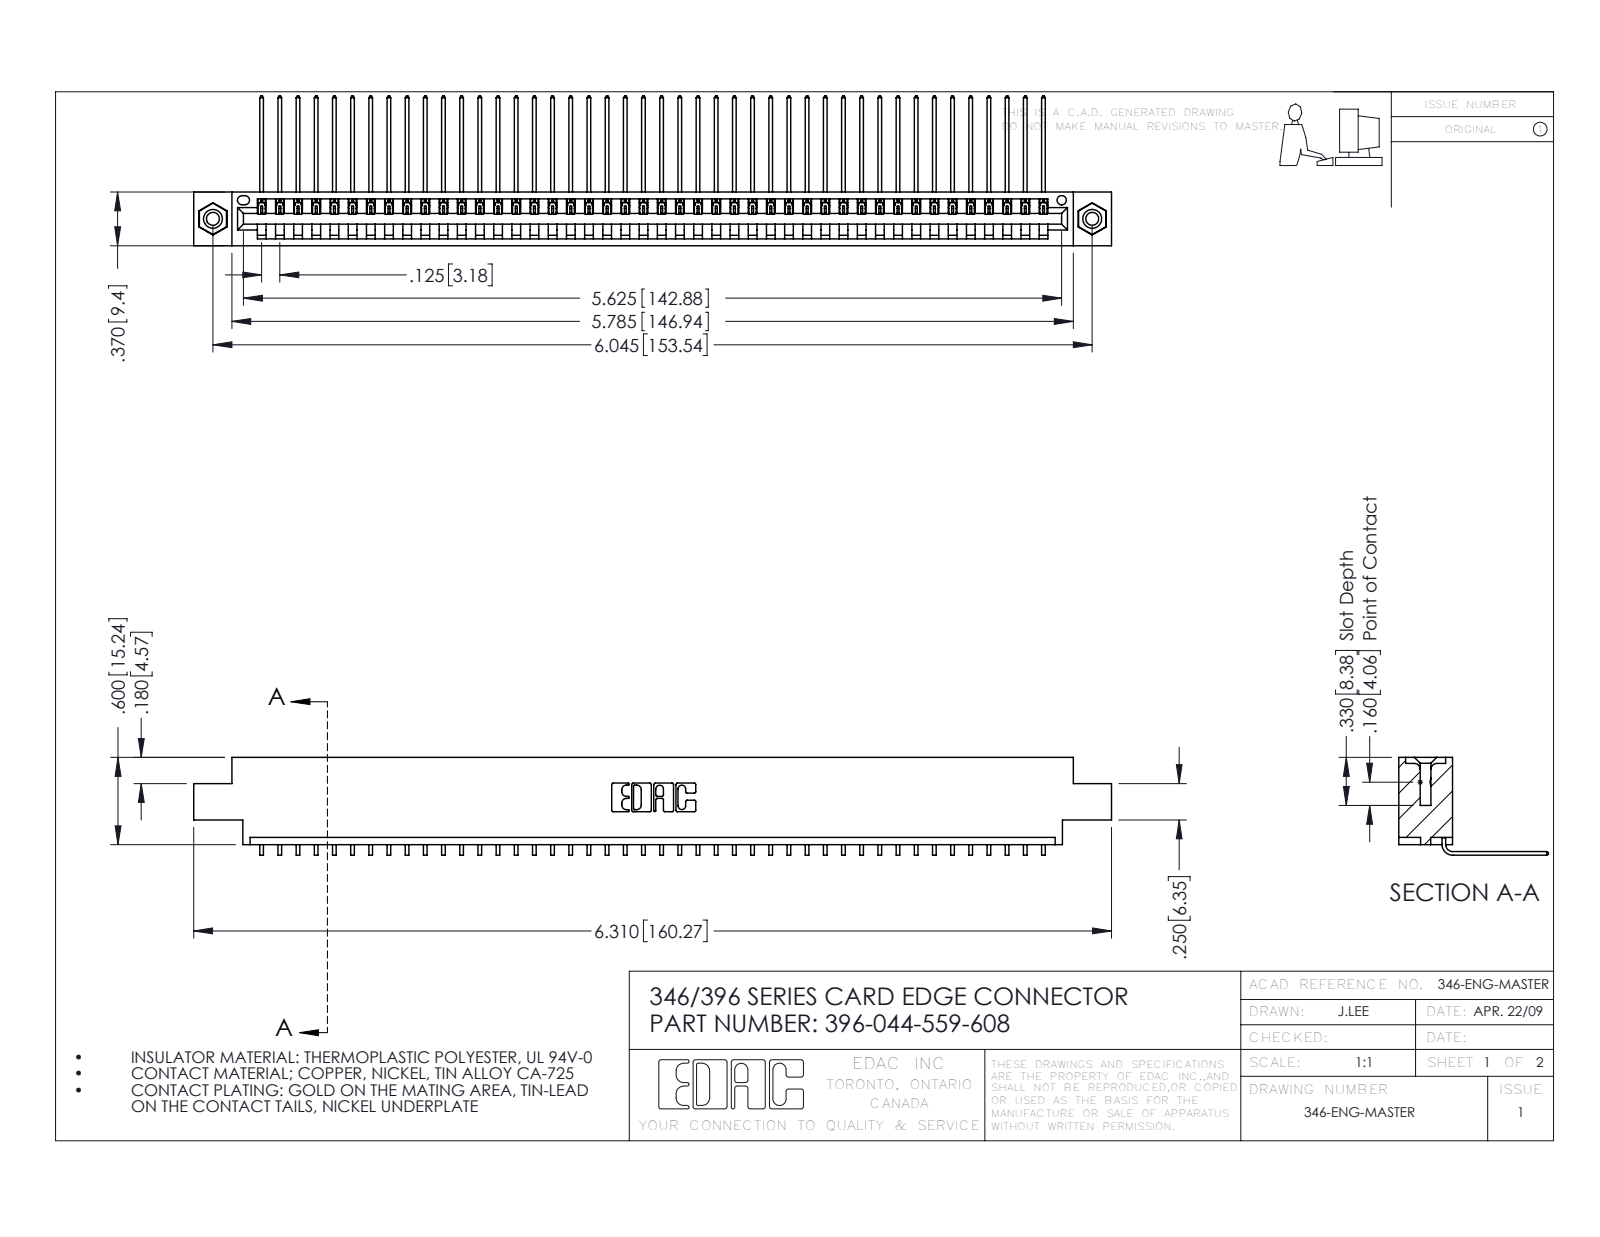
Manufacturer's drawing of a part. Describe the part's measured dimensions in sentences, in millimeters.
The part is named "345-250-001_345-250-003-102; 345-292-001_558 559 Tail - 1; 396-044-559-608; 346 Part_0.170 Offset - 0.156 Dia-TI". Its 3-D file was written by "SolidWorks 2016 (CONFIG_CONTROL_DESIGN)". It is 47 solids with 2826 faces: 1960 planar, 850 cylindrical and 16 other. Overall it measures 160.3 by 26.2 by 17.1 millimeters. Its volume is 15 300 cubic millimeters and its surface area 20 250 square millimeters. Round holes: 2 of diameter 2.3, 2 of diameter 3.2, 2 of diameter 4, 1 of diameter 1.6. Round bosses or shafts: 2 of diameter 3.9. Partial cylindrical surfaces (rounded edges, fillets, slot ends): 88 of radius 0.2, 22 of radius 0.3, 6 of radius 0.2, 6 of radius 0.8, 3 of radius 0.7, 2 of radius 0.8, 2 of radius 1, 1 of radius 0.4. The main face-to-face distances are 1.2, 8.2, 9.4, 0.6, 6.4, 1.8, 5.6, 3.8, 7.6, 2.5. The hole center spacings are 6.2, 148.2, 153.5.
